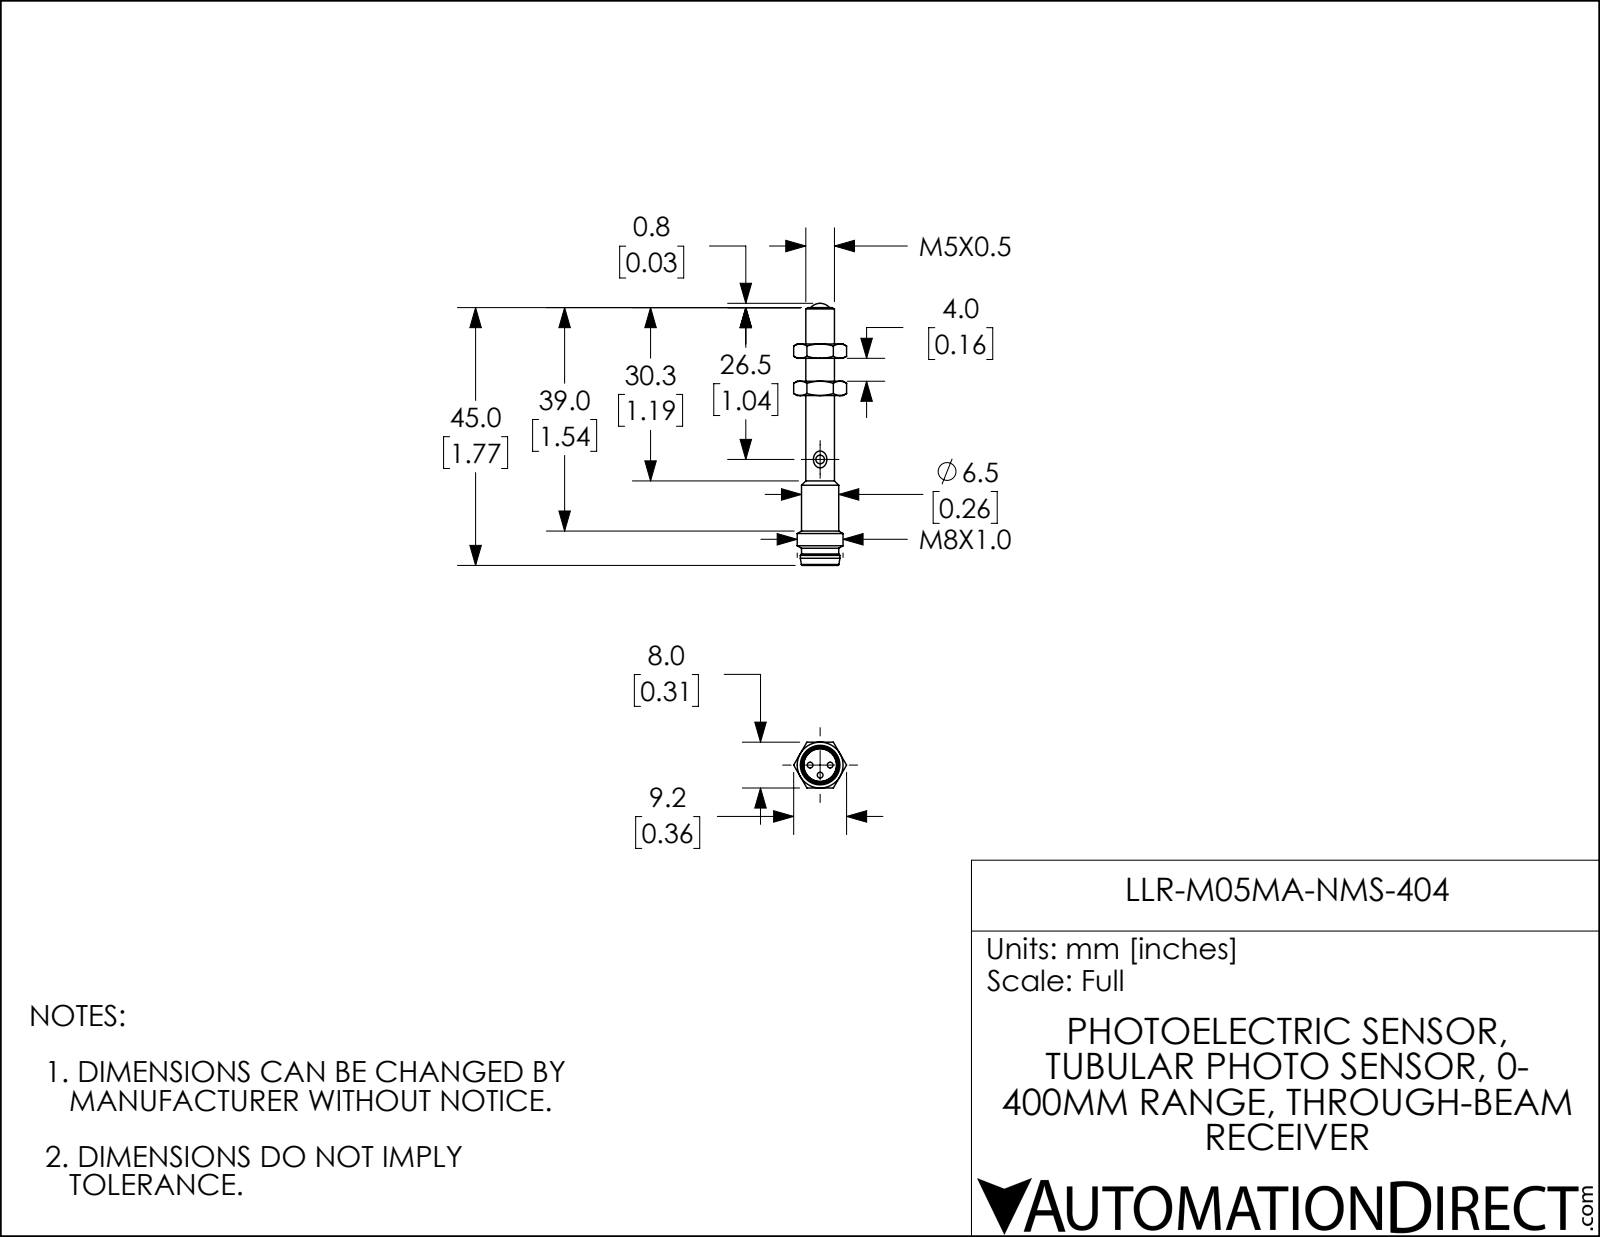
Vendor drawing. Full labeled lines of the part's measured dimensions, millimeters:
Part name (STEP PRODUCT): LLR-M05MA-NMS-404
STEP written by: SolidWorks 2018 (AUTOMOTIVE_DESIGN)
Units: millimetres
Bodies: 3 solids, 76 faces (20 planar, 15 cylindrical, 41 other)
Overall size (bounding box): 45.7 × 9.2 × 8
Volume: 1 200 mm³ · Surface area: 1 341 mm²
Round holes (diameter × count): ⌀1.5 ×1, ⌀5 ×1, ⌀5.8 ×1
Round bosses / shafts (diameter × count): ⌀1 ×3, ⌀8 ×1, ⌀6.9 ×1, ⌀6.5 ×1, ⌀5.7 ×1
Partial cylindrical surfaces — rounded edges, fillets, slot ends (radius × count): R1.8 ×1
Main face-to-face distances: 8, 6.5, 2.5, 9, 4, 24.7, 27.2, 31.2, 33.7, 40.1
